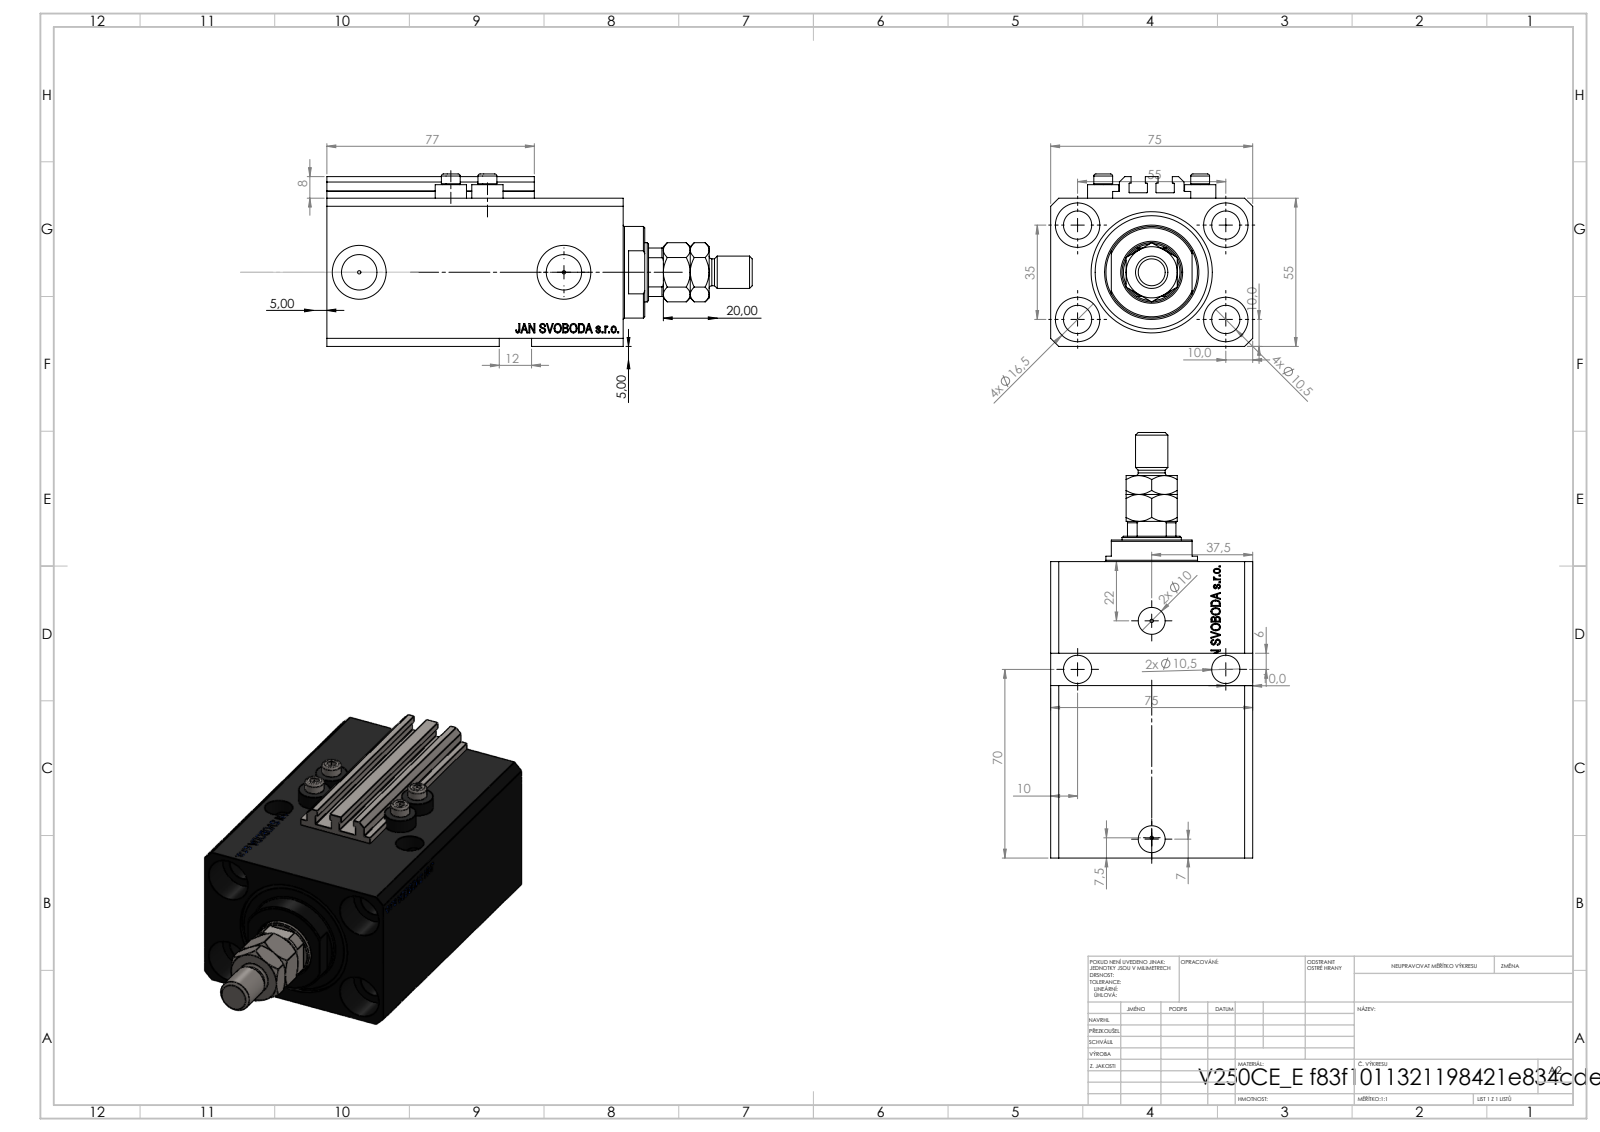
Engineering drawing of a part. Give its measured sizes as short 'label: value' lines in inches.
name: V250CE_C_VCP; MTA; V250CE_E_Body; ALLEN BOLT V250CE (+1 more)
written by: SolidWorks 2019 (CONFIG_CONTROL_DESIGN)
unit: in
bodies: 9 solids, 1133 faces (529 planar, 150 cylindrical, 454 other)
size: 6.22 × 2.953 × 2.52
volume: 23.7 in³; area: 151.8 in²
holes: 9× ⌀0.413, 4× ⌀0.049, 4× ⌀0.157, 4× ⌀0.65, 2× ⌀0.394, 2× ⌀0.518, 2× ⌀0.787, 1× ⌀0.866, 1× ⌀1.26, 1× ⌀1.772
bosses: 4× ⌀0.457, 4× ⌀0.276, 1× ⌀1.339, 1× ⌀0.472, 1× ⌀0.394
rounds: 10× R0.008, 1× R0.413
face distances: 2.165, 2.953, 0.591, 4.331, 3.74, 0.118, 0.39, 3.35, 3.941, 0.098
hole spacings: 1.283, 1.294, 2.165, 2.706, 0.535, 0.555, 0.907, 1.016
